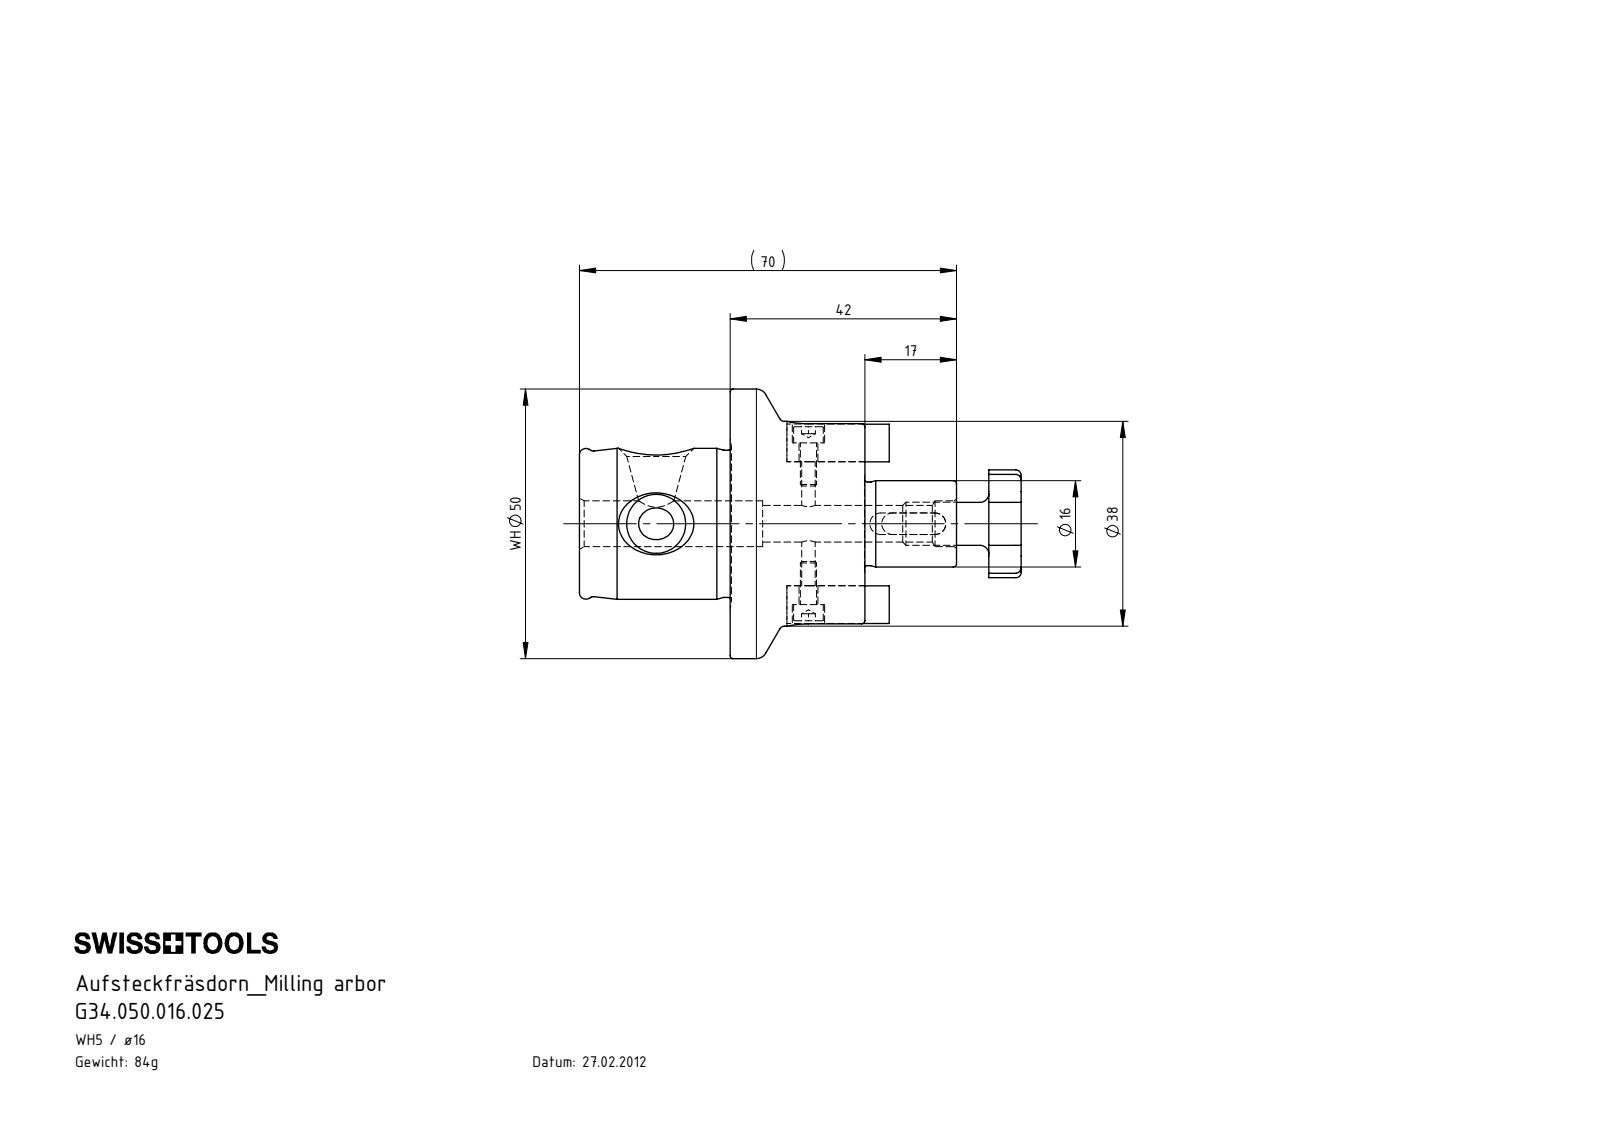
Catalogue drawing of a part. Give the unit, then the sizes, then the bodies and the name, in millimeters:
Units: millimetres
Overall size (bounding box): 82 × 50 × 50
Round holes (diameter × count): ⌀2.5 ×1, ⌀3.5 ×1, ⌀6 ×1, ⌀6.8 ×1, ⌀8.5 ×1
Round bosses / shafts (diameter × count): ⌀50 ×1, ⌀38 ×1, ⌀28 ×1, ⌀27.3 ×1, ⌀16 ×1, ⌀15.5 ×1, ⌀8 ×1, ⌀5.5 ×1
Partial cylindrical surfaces — rounded edges, fillets, slot ends (radius × count): R2 ×7, R4 ×1, R10 ×1
Main face-to-face distances: 25, 28, 53, 8, 23, 6, 7, 30, 82, 54
Volume: 53 086 mm³ · Surface area: 15 771 mm²
Bodies: 7 solids, 210 faces (71 planar, 60 cylindrical, 79 other)
Part name (STEP PRODUCT): ISO 4762 - M3 x 8; WH5-D16.001.025; WH5.D16.001.025; D16-ER1.001.016_A (+2 more)
STEP written by: SolidWorks 2022 (AUTOMOTIVE_DESIGN)
